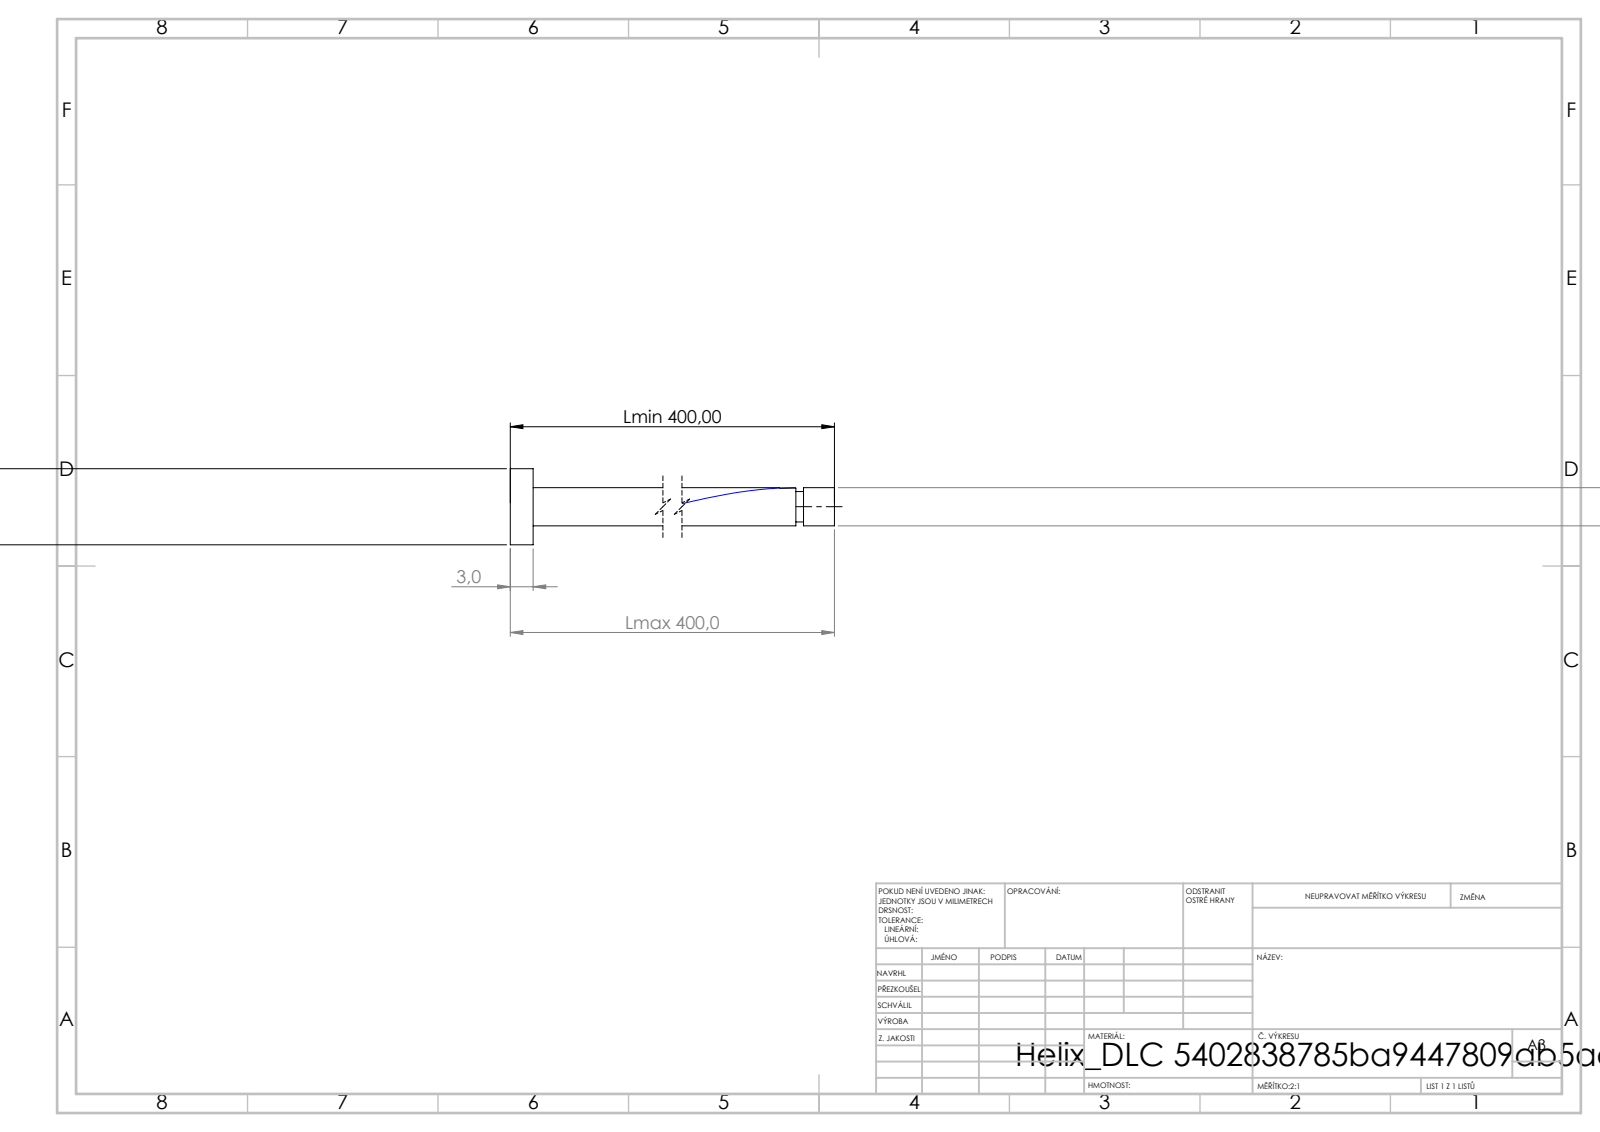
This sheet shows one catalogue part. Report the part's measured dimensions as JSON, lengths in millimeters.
{"step_written_by": "SolidWorks 2019 (CONFIG_CONTROL_DESIGN)", "units": "millimeters", "bodies": {"solids": 1, "faces": 16, "planar": 6, "cylindrical": 9, "other": 1}, "overall_size": [400, 10, 10], "volume_mm3": 9695, "surface_area_mm2": 8691, "round_bosses_or_shafts": [[10, 1], [5, 1], [4, 1]], "face_to_face_distances": [3, 400, 397, 395.93, 392.93, 4.07, 394.93, 391.93, 1, 5.07]}
